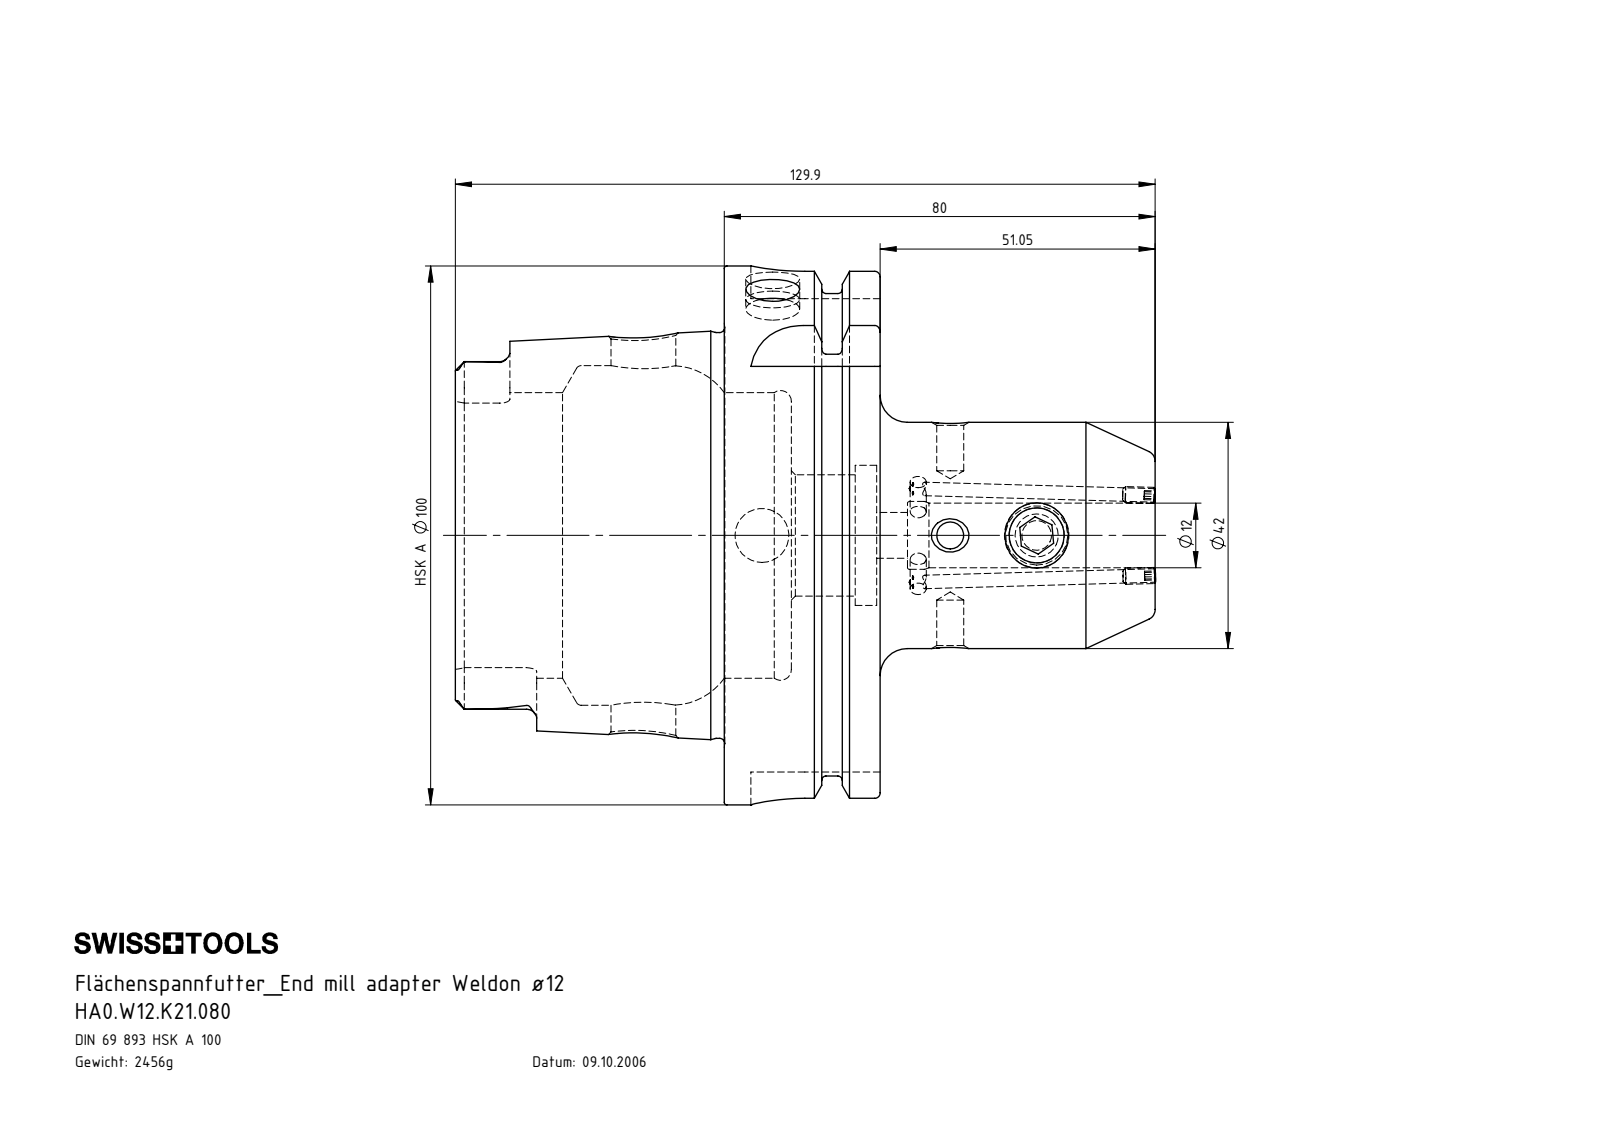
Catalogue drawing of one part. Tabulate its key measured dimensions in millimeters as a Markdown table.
| quantity | value |
| --- | --- |
| part name | HA0.W12.K21.080; ERU-CJ2.001.006; W12-ER1.001.016; HA0-W12.K21.080_C_Fertigbearbeitung |
| STEP written by | SolidWorks 2012 (CONFIG_CONTROL_DESIGN) |
| units | millimeters |
| bodies | 4 solids, 271 faces (71 planar, 82 cylindrical, 118 other) |
| overall size | 129.98 × 100 × 100 |
| volume | 312 910 mm³ |
| surface area | 60 147 mm² |
| round holes (diameter × count) | 10 × 3, 2.5 × 2, 5 × 2, 12 × 2, 3 × 1, 8.5 × 1, 10.25 × 1, 12.6 × 1, 22.5 × 1, 26 × 1, 53 × 1, 63 × 1 |
| round bosses / shafts (diameter × count) | 3 × 2, 100 × 1, 91.95 × 1, 75.26 × 1, 42 × 1, 12 × 1 |
| partial cylindrical surfaces (radius × count) | 1.9 × 6, 4.88 × 4, 10 × 4 |
| main face-to-face distances | 28.95, 16.5, 12.45, 49.9, 62.35, 78.85, 78.2, 28.3, 15.85, 0.65 |
| hole center spacings | 16.05, 34.95, 51, 56.95 |
